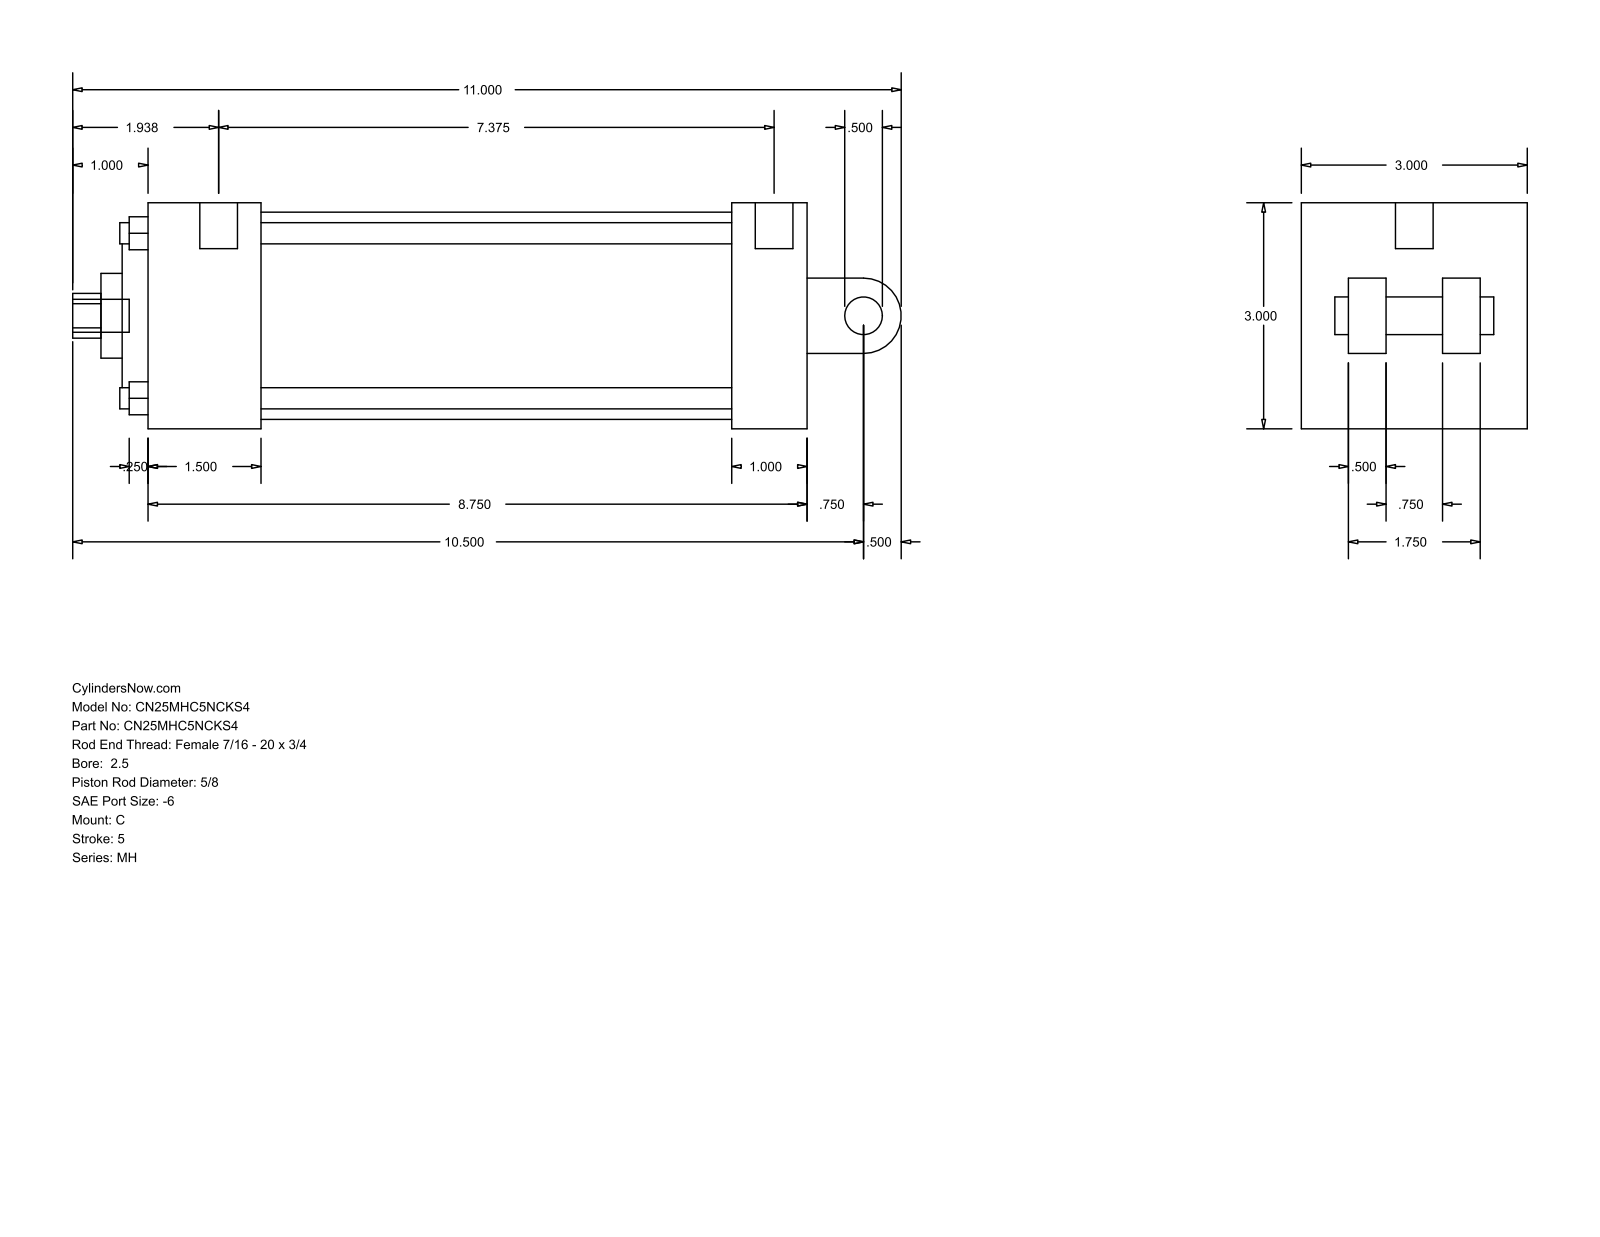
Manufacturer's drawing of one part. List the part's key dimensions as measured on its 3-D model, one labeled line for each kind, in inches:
Part name (STEP PRODUCT): MH_C__0250_0.625
STEP written by: GSSL Pune (CONFIG_CONTROL_DESIGN)
Units: inches
Bodies: 0 solids, 101 faces (71 planar, 30 cylindrical, 0 other)
Overall size (bounding box): 11 × 3 × 3
Round holes (diameter × count): ⌀0.281 ×4, ⌀0.219 ×2, ⌀0.5 ×1, ⌀0.625 ×1, ⌀1.125 ×1, ⌀2.187 ×1, ⌀2.75 ×1
Round bosses / shafts (diameter × count): ⌀0.5 ×2, ⌀0.219 ×2, ⌀0.437 ×1
Partial cylindrical surfaces — rounded edges, fillets, slot ends (radius × count): R0.297 ×1, R0.5 ×1
Main face-to-face distances: 3, 1, 8.75, 0.625, 7.75, 1.5, 6.25, 7.25, 0.344, 1.844
Hole centre spacings: 1.548, 2.19, 3.097, 0.125
